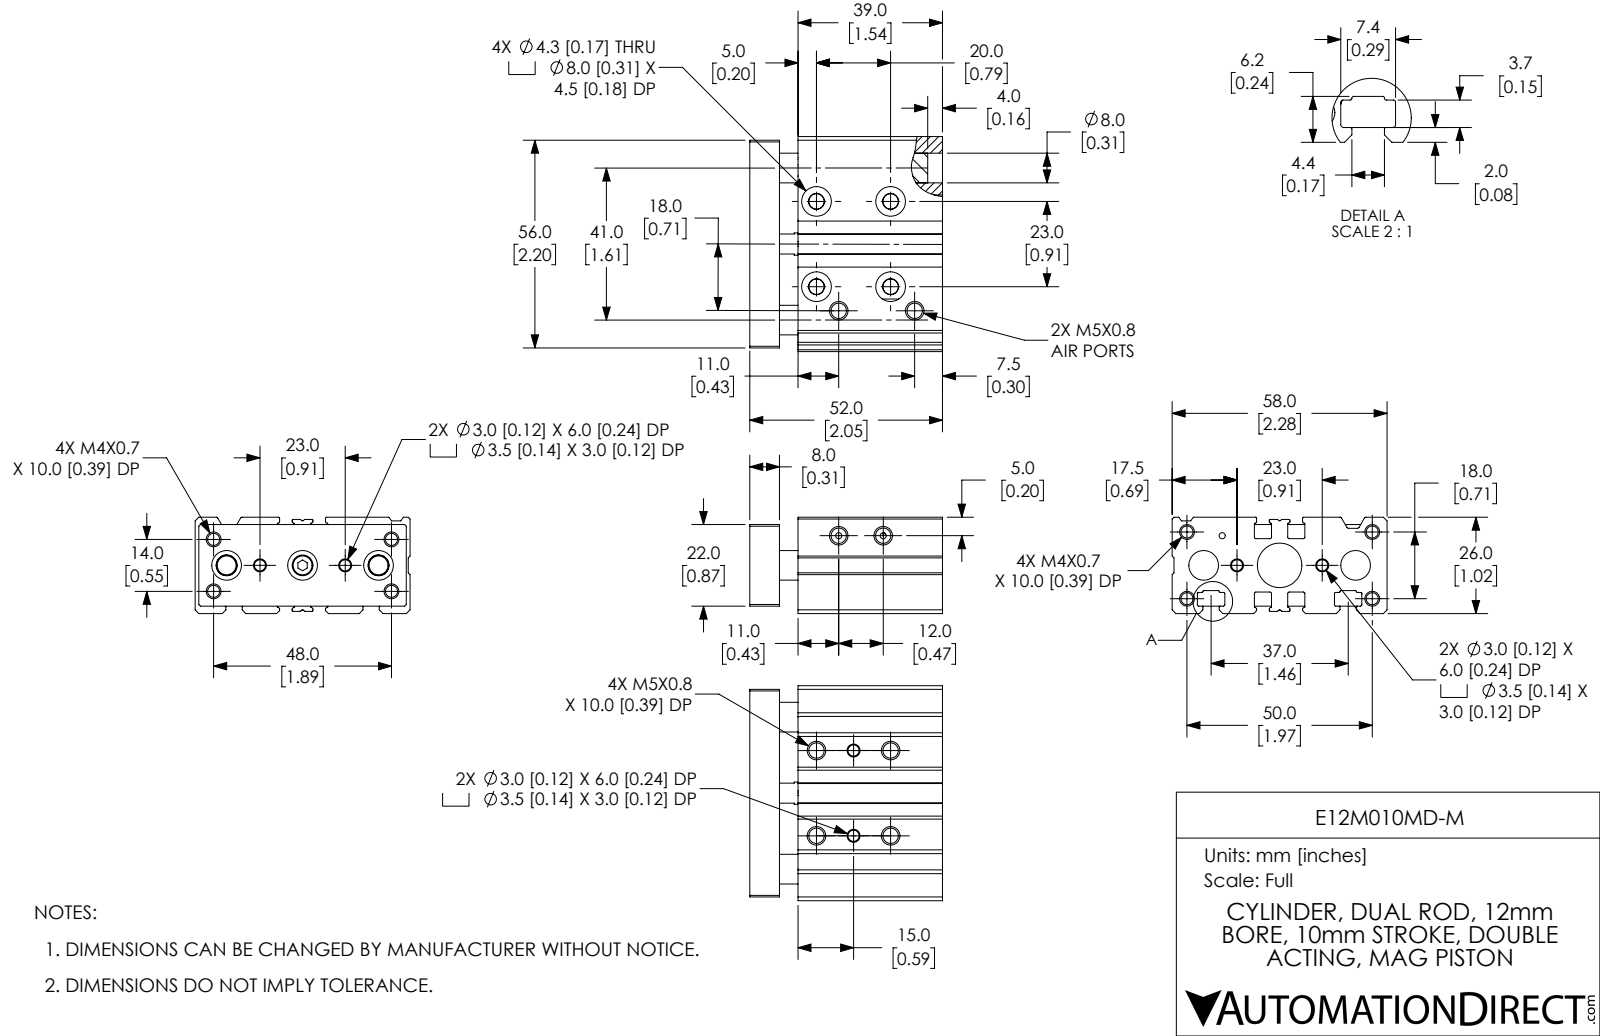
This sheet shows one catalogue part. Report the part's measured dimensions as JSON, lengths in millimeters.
{"part_name": "E12M010MD-M; E12M010MD-M_BODY; E12M010MD-M_ENDPLATE", "step_written_by": "SolidWorks 2019 (CONFIG_CONTROL_DESIGN)", "units": "millimeters", "bodies": {"solids": 5, "faces": 413, "planar": 137, "cylindrical": 188, "other": 88}, "overall_size": [58, 52, 26], "volume_mm3": 55971, "surface_area_mm2": 26695, "round_holes": [[3.24, 8], [4.13, 8], [8, 7], [3, 4], [3.5, 4], [4.3, 4], [1.67, 3], [4, 3], [5.59, 2], [8, 1], [12, 1], [12, 1]], "round_bosses_or_shafts": [[6, 1], [5.59, 1]], "partial_cylinders_radius": [[0.4, 20], [0.2, 18], [0.25, 8], [0.3, 6], [0.5, 4]], "face_to_face_distances": [8, 2, 44, 13, 5, 26, 24, 39, 52, 5.8], "hole_center_spacings": [2.24, 7.83, 10, 10.06, 14.33, 16.03, 16.22, 23]}
